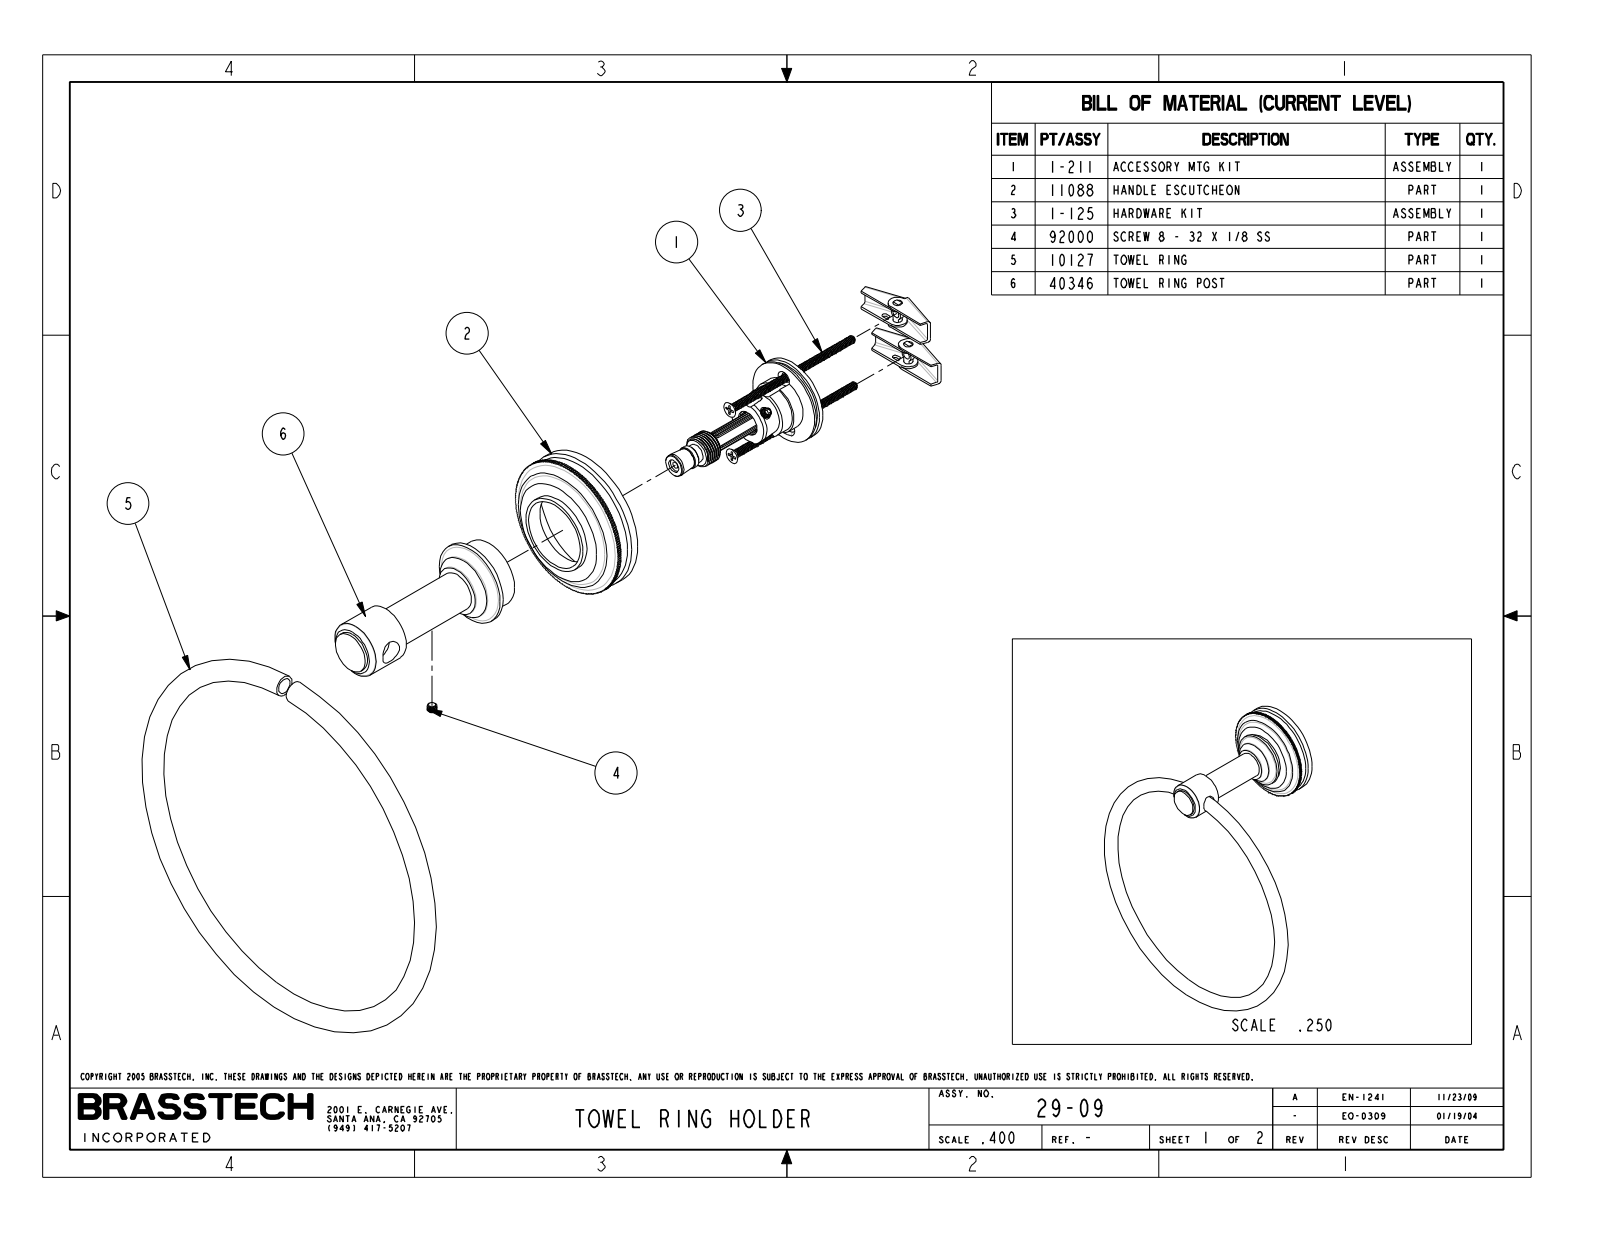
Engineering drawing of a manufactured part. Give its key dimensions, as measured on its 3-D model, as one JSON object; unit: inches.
{"part_name": "29-09_WEB", "step_written_by": "PRO/ENGINEER BY PARAMETRIC TECHNOLOGY CORPORATION, 2009300 (CONFIG_CONTROL_DESIGN)", "units": "inches", "bodies": {"solids": 0, "faces": 575, "planar": 358, "cylindrical": 200, "other": 17}, "overall_size": [8.06, 7, 3.75], "round_bosses_or_shafts": [[2.5, 1], [2.4, 1], [1.48, 1], [1.38, 1], [1.134, 1], [1, 1], [0.88, 1], [0.725, 1]], "partial_cylinders_radius": [[0.203, 1]], "face_to_face_distances": [0.1, 0.475, 0.4, 0.075, 0.2, 0.575, 0.175, 0.675, 0.275, 0.075]}
